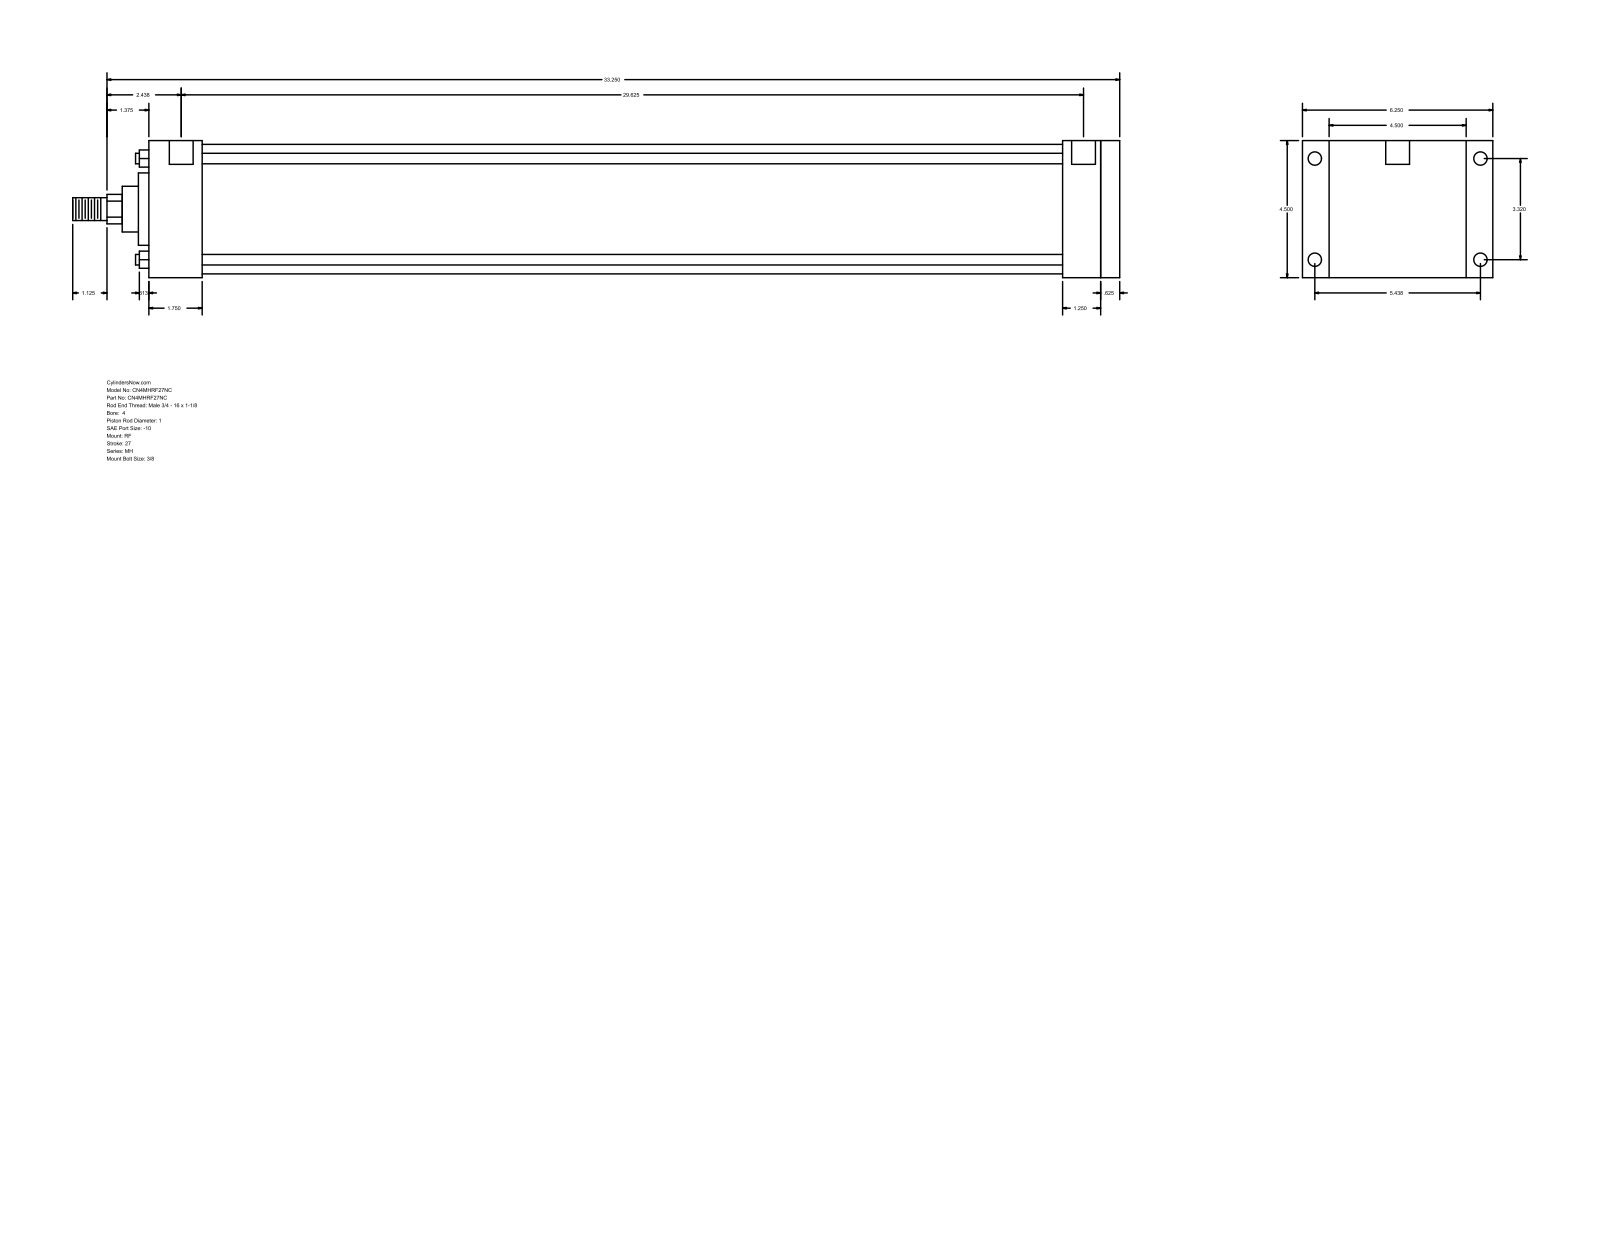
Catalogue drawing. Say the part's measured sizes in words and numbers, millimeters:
The part is named "MH_RF__0400_1". Its 3-D file was written by "GSSL Pune (CONFIG_CONTROL_DESIGN)". It is 0 solids with 94 faces: 65 planar, 29 cylindrical and 0 other. Overall it measures 873.12 by 158.75 by 114.3 millimeters. Round holes: 4 of diameter 8.73, 4 of diameter 11.13, 2 of diameter 19.84. Round bosses or shafts: 4 of diameter 8.76, 1 of diameter 107.95, 1 of diameter 60.33, 1 of diameter 38.1, 1 of diameter 25.4, 1 of diameter 19.05. Partial cylindrical surfaces (rounded edges, fillets, slot ends): 1 of radius 12.29. The main face-to-face distances are 114.3, 809.63, 793.75, 15.88, 47.63, 44.46, 749.29, 765.17, 762, 717.54. The hole center spacings are 84.32, 138.12, 161.82, 755.65, 1.58, 1.59, 752.48, 754.06.
